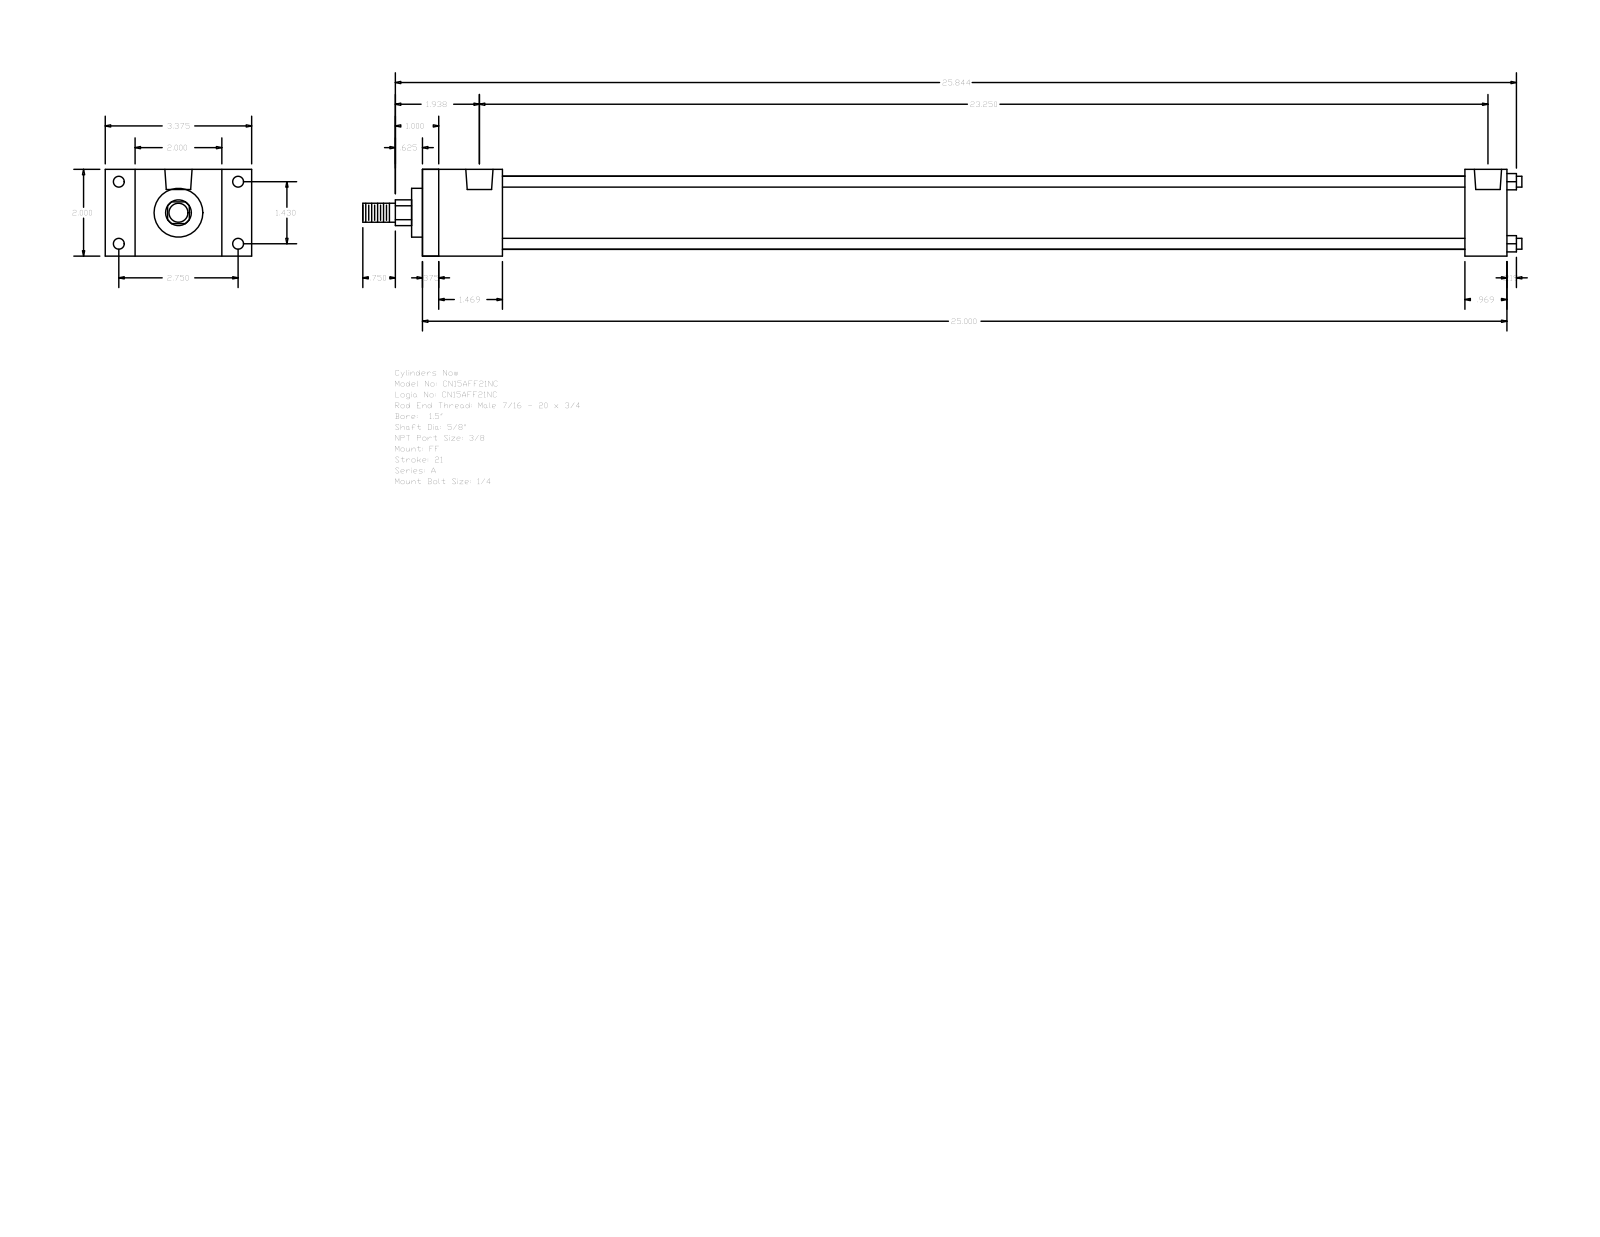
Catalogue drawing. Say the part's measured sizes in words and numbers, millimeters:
The part is named "A_FF__0150_0.625". Its 3-D file was written by "GSSL Pune (CONFIG_CONTROL_DESIGN)". It is 0 solids with 92 faces: 64 planar, 28 cylindrical and 0 other. Overall it measures 678.66 by 85.72 by 50.8 millimeters. Round holes: 4 of diameter 5.56, 4 of diameter 6.35, 2 of diameter 15.93. Round bosses or shafts: 4 of diameter 6.35, 1 of diameter 42.93, 1 of diameter 28.57, 1 of diameter 15.88, 1 of diameter 11.11. Partial cylindrical surfaces (rounded edges, fillets, slot ends): 1 of radius 7.54. The main face-to-face distances are 50.8, 635, 9.52, 625.48, 46.83, 610.39, 37.31, 600.87, 563.56, 588.17. The hole center spacings are 3.97, 36.32, 69.84, 78.72, 582.61, 586.58, 590.55.
